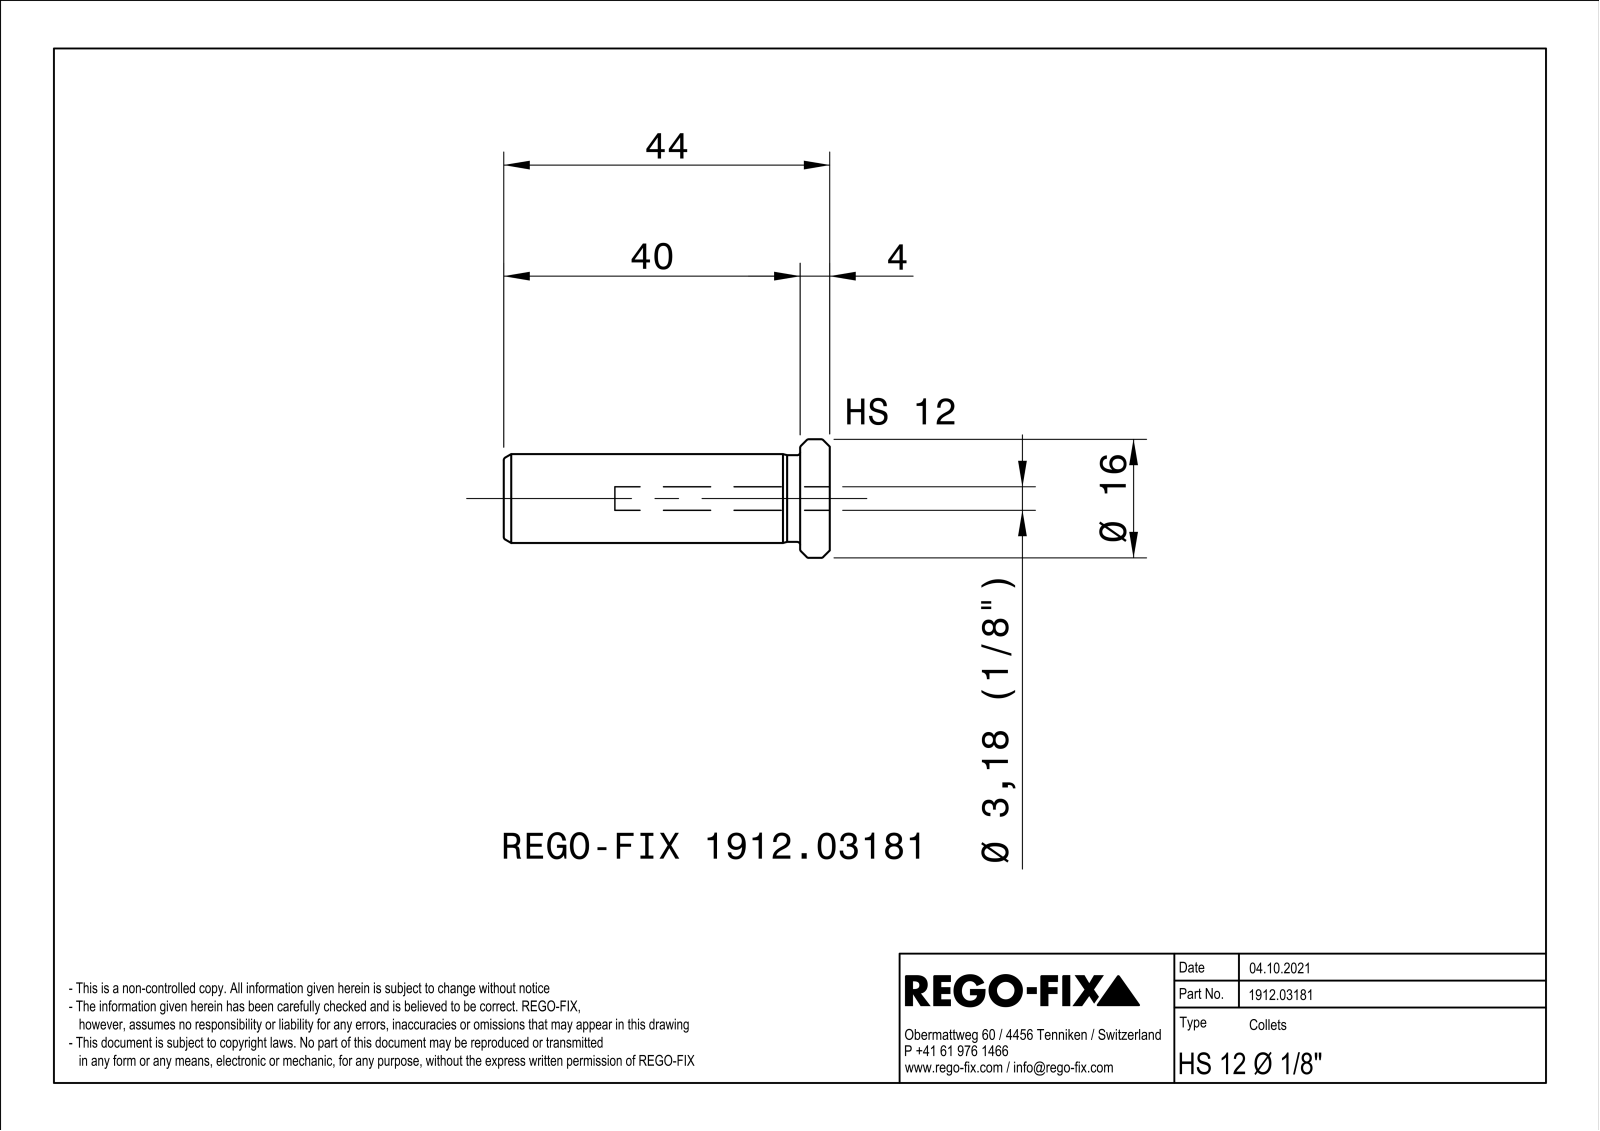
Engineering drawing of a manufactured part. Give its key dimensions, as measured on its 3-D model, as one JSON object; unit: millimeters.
{"part_name": "NOCUT", "step_written_by": "SIEMENS PLM Software Solid Edge ST10 (AUTOMOTIVE_DESIGN)", "units": "millimeters", "bodies": {"solids": 1, "faces": 70, "planar": 14, "cylindrical": 11, "other": 45}, "overall_size": [44, 15.98, 15.98], "volume_mm3": 4012, "surface_area_mm2": 3506, "round_holes": [[3.17, 1], [7.5, 1]], "round_bosses_or_shafts": [[16, 1], [12, 1], [11.7, 1]], "face_to_face_distances": [0.8, 44, 4, 40]}
